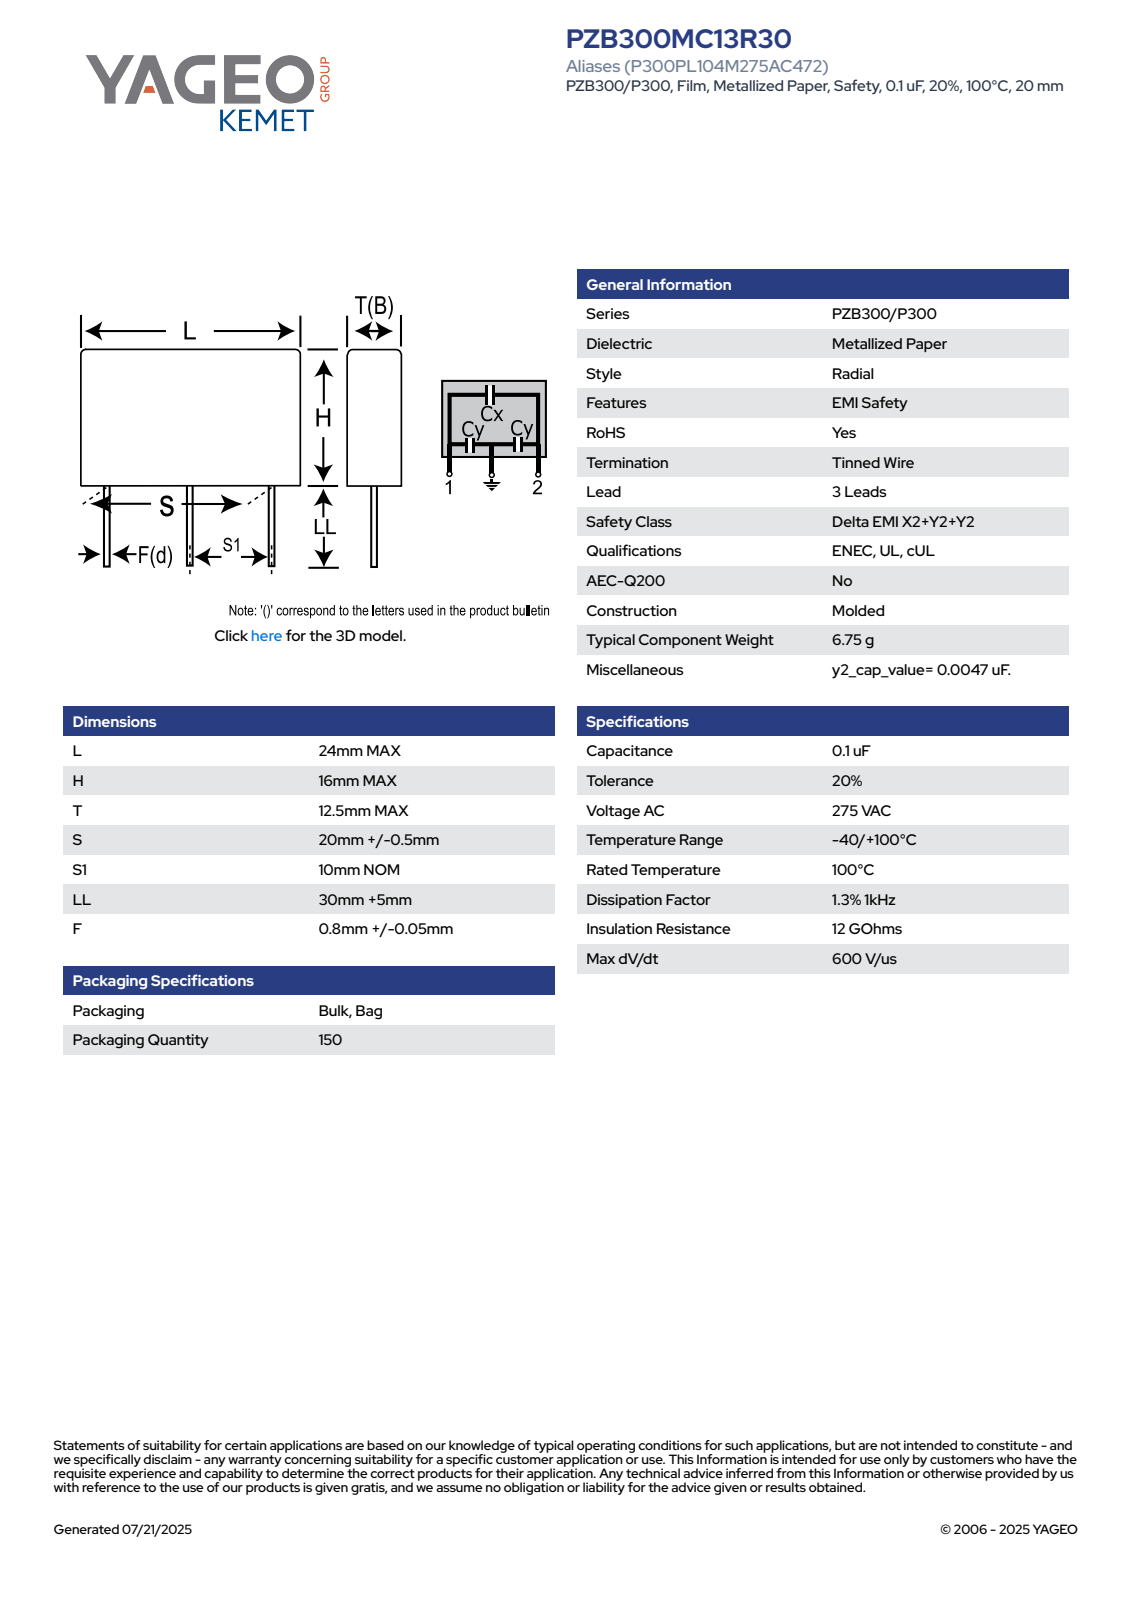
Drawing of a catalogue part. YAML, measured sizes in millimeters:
part_name: "CFR_PZB300_24X16X12.5L24H16T12.5S20S110LL35F0.85"
step_written_by: "SolidWorks 2014 (AUTOMOTIVE_DESIGN)"
units: millimeters
bodies: {solids: 4, faces: 76, planar: 66, cylindrical: 10, other: 0}
overall_size: [51, 24, 12.51]
volume: 4854
surface_area: 2064
round_bosses_or_shafts:
  - {diameter: 0.85, count: 3}
partial_cylinders:
  - {radius: 0.6, count: 4}
face_to_face_distances: [12.5, 16, 24, 12.51, 35, 51, 6.81, 44.19, 9.19, 41.77]
